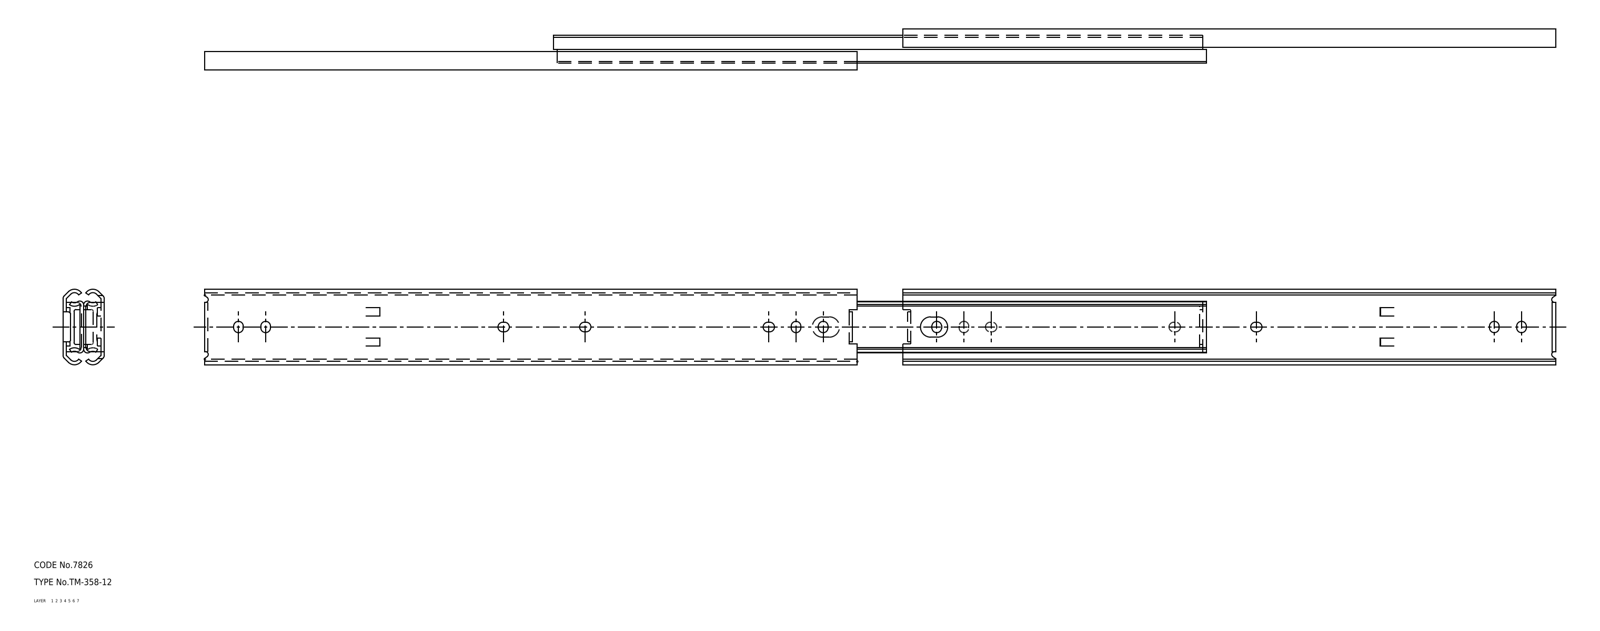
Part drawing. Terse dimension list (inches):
name: member_B; member_A1^TM_358_12; TM_358_12
written by: SolidWorks 2015 (AUTOMOTIVE_DESIGN)
unit: in
bodies: 3 solids, 212 faces (122 planar, 90 cylindrical, 0 other)
size: 24.835 × 1.39 × 0.756
volume: 4.612 in³; area: 135.7 in²
rounds: 28× R0.089, 10× R0.063, 8× R0.039, 8× R0.094, 8× R0.157, 4× R0.008, 4× R0.051, 4× R0.071
face distances: 0.063, 0.693, 0.315, 0.378, 0.441, 0.252, 0.63, 0.756, 0.126, 1.252
